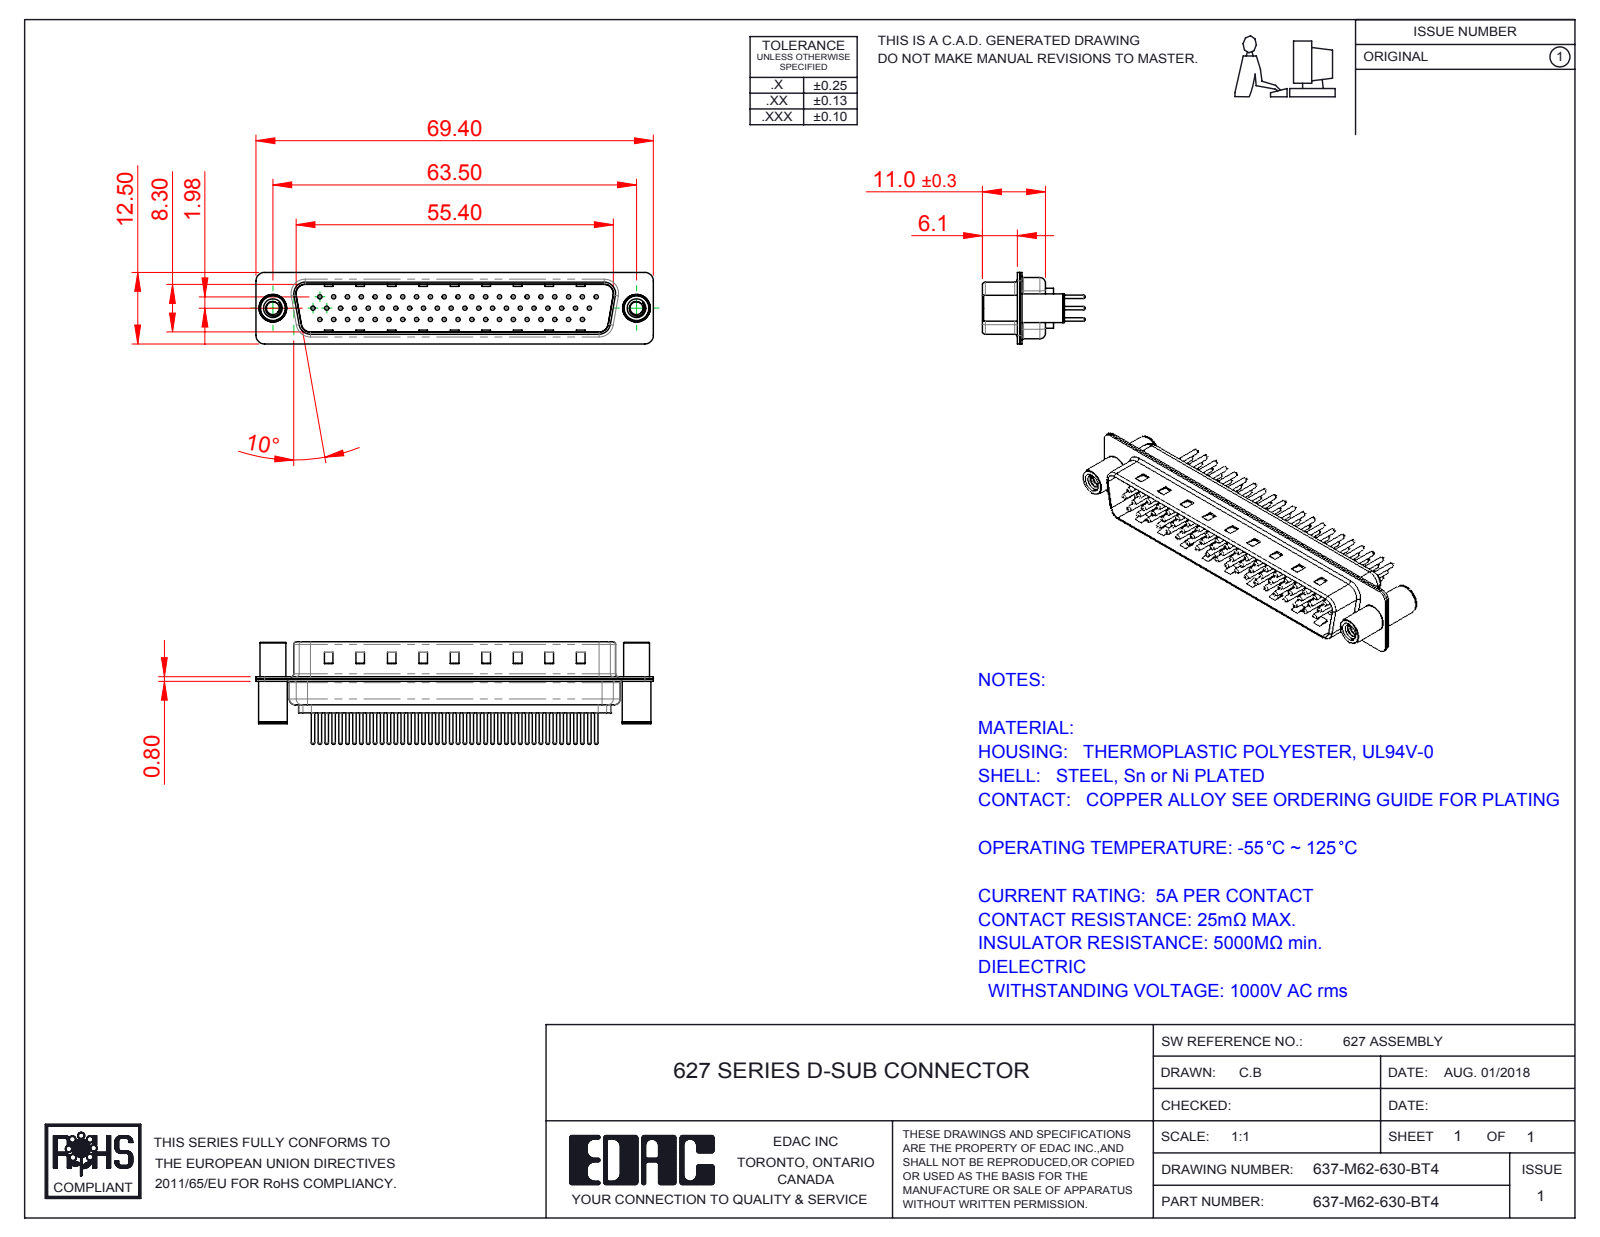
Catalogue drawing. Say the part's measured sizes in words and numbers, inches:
The part is named "637M Housing_62 Contacts; 637-M62-630-BT4; 637M Contact Row 2_30; 637M Contact Row 3_30 (+4 more)". Its 3-D file was written by "SolidWorks 2016 (CONFIG_CONTROL_DESIGN)". It is 67 solids with 2792 faces: 643 planar, 1061 cylindrical and 1088 other. Overall it measures 2.732 by 0.705 by 0.492 inches. Its volume is 0.257 cubic inches and its surface area 18.51 square inches. Round holes: 62 of diameter 0.03, 62 of diameter 0.063, 62 of diameter 0.079, 2 of diameter 0.089, 2 of diameter 0.128, 2 of diameter 0.157, 2 of diameter 0.189. Round bosses or shafts: 62 of diameter 0.059, 62 of diameter 0.024, 2 of diameter 0.197, 2 of diameter 0.193, 2 of diameter 0.177. Partial cylindrical surfaces (rounded edges, fillets, slot ends): 16 of radius 0.059, 12 of radius 0.079, 8 of radius 0.02, 8 of radius 0.063, 4 of radius 0.01, 4 of radius 0.024, 4 of radius 0.026, 4 of radius 0.035. The main face-to-face distances are 0.016, 0.031, 0.374, 0.358, 0.343, 0.39, 0.03, 0.014, 0.232, 0.047. The hole center spacings are 0.285, 0.091, 0.095, 0.163, 0.38, 0.19, 0.57, 0.435.
